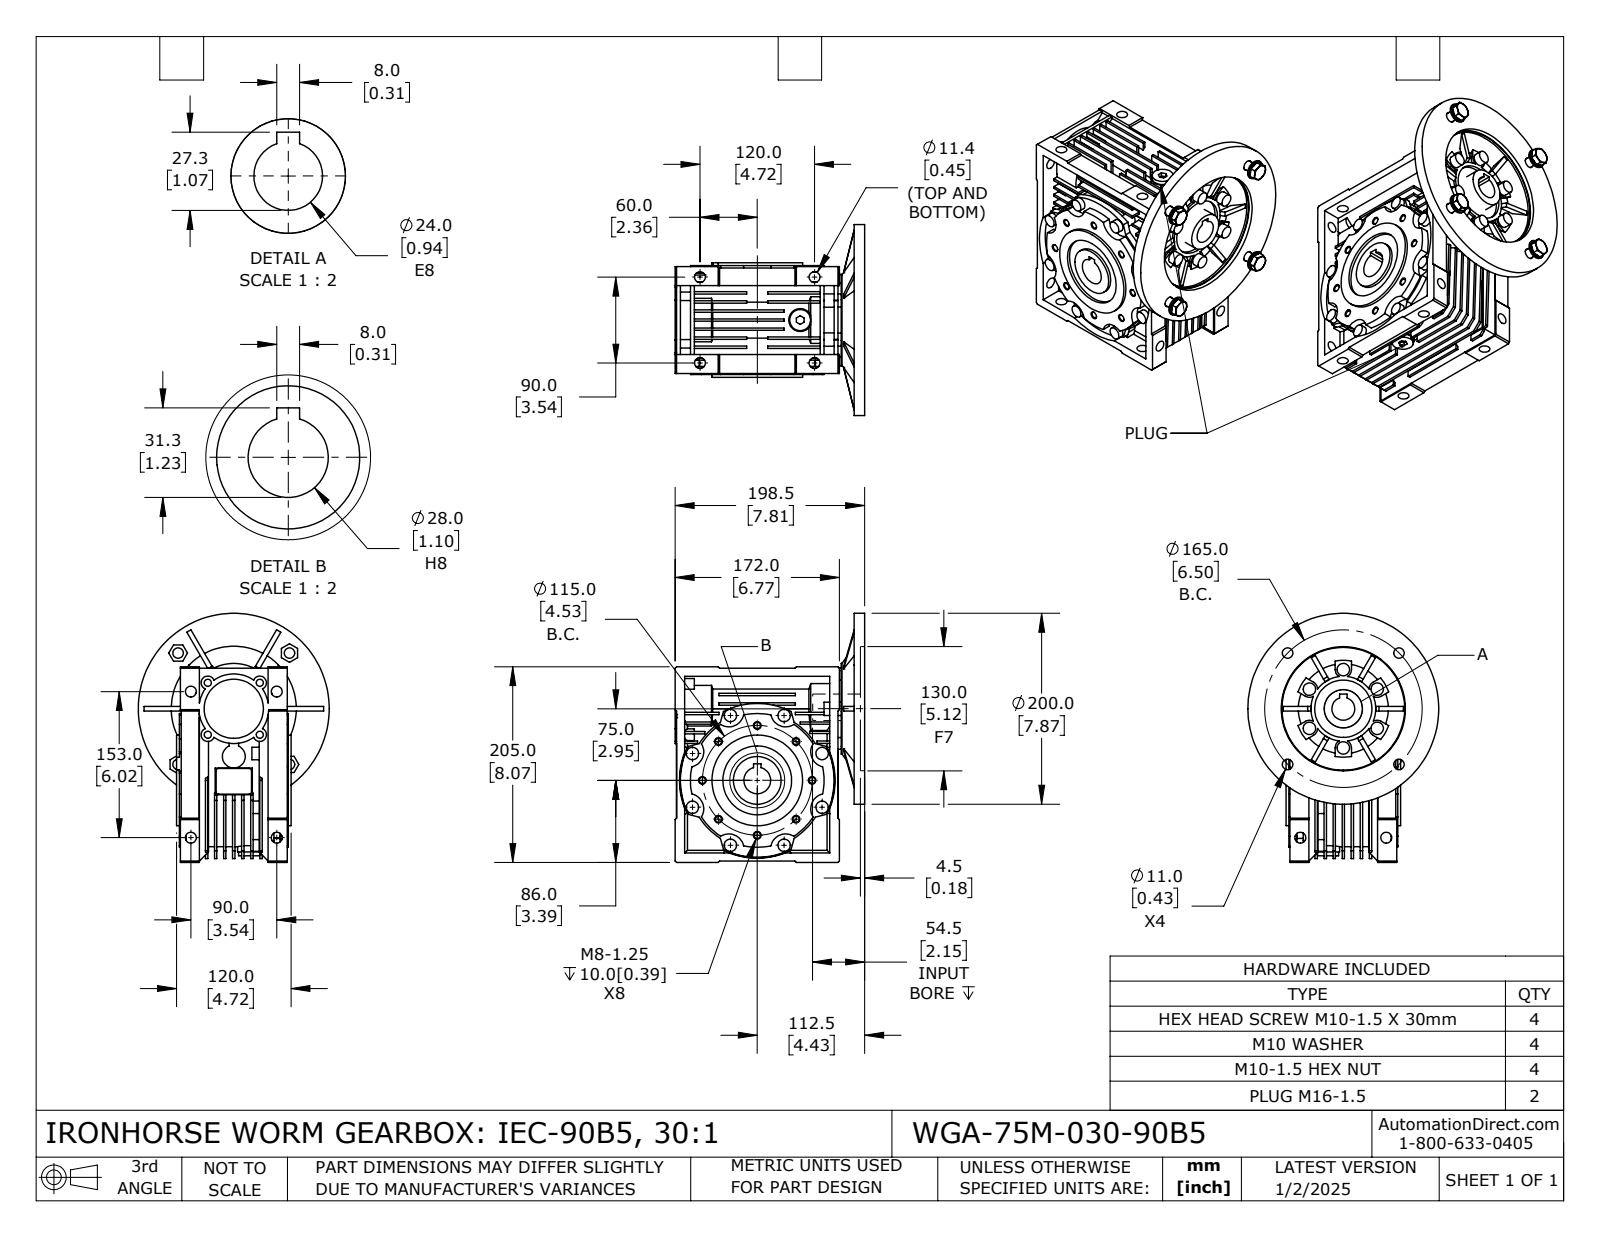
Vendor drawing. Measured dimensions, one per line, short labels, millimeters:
name: WGA-75M-030-90B5
written by: SolidWorks 2024 (CONFIG_CONTROL_DESIGN)
unit: mm
bodies: 20 solids, 1475 faces (818 planar, 439 cylindrical, 218 other)
size: 261 × 216.93 × 200
volume: 3 036 000 mm³; area: 538 373 mm²
holes: 8× ⌀6.65, 8× ⌀11.38, 4× ⌀7.45, 4× ⌀8.5, 4× ⌀10, 4× ⌀10.5, 4× ⌀11, 2× ⌀14.5, 1× ⌀24, 1× ⌀25, 1× ⌀28, 1× ⌀39
bosses: 14× ⌀13, 4× ⌀20, 4× ⌀16, 3× ⌀24, 2× ⌀95, 2× ⌀22, 2× ⌀15.8, 2× ⌀13.7
rounds: 10× R7, 8× R16, 6× R8.5, 4× R2.5, 1× R33.99, 1× R36, 1× R36.5, 1× R39
face distances: 9.5, 2.5, 19, 12, 7, 28.5, 10, 16.5, 27.75, 21.5
hole spacings: 44.01, 57.5, 81.32, 91.04, 106.25, 38.49, 54.44, 82.51
